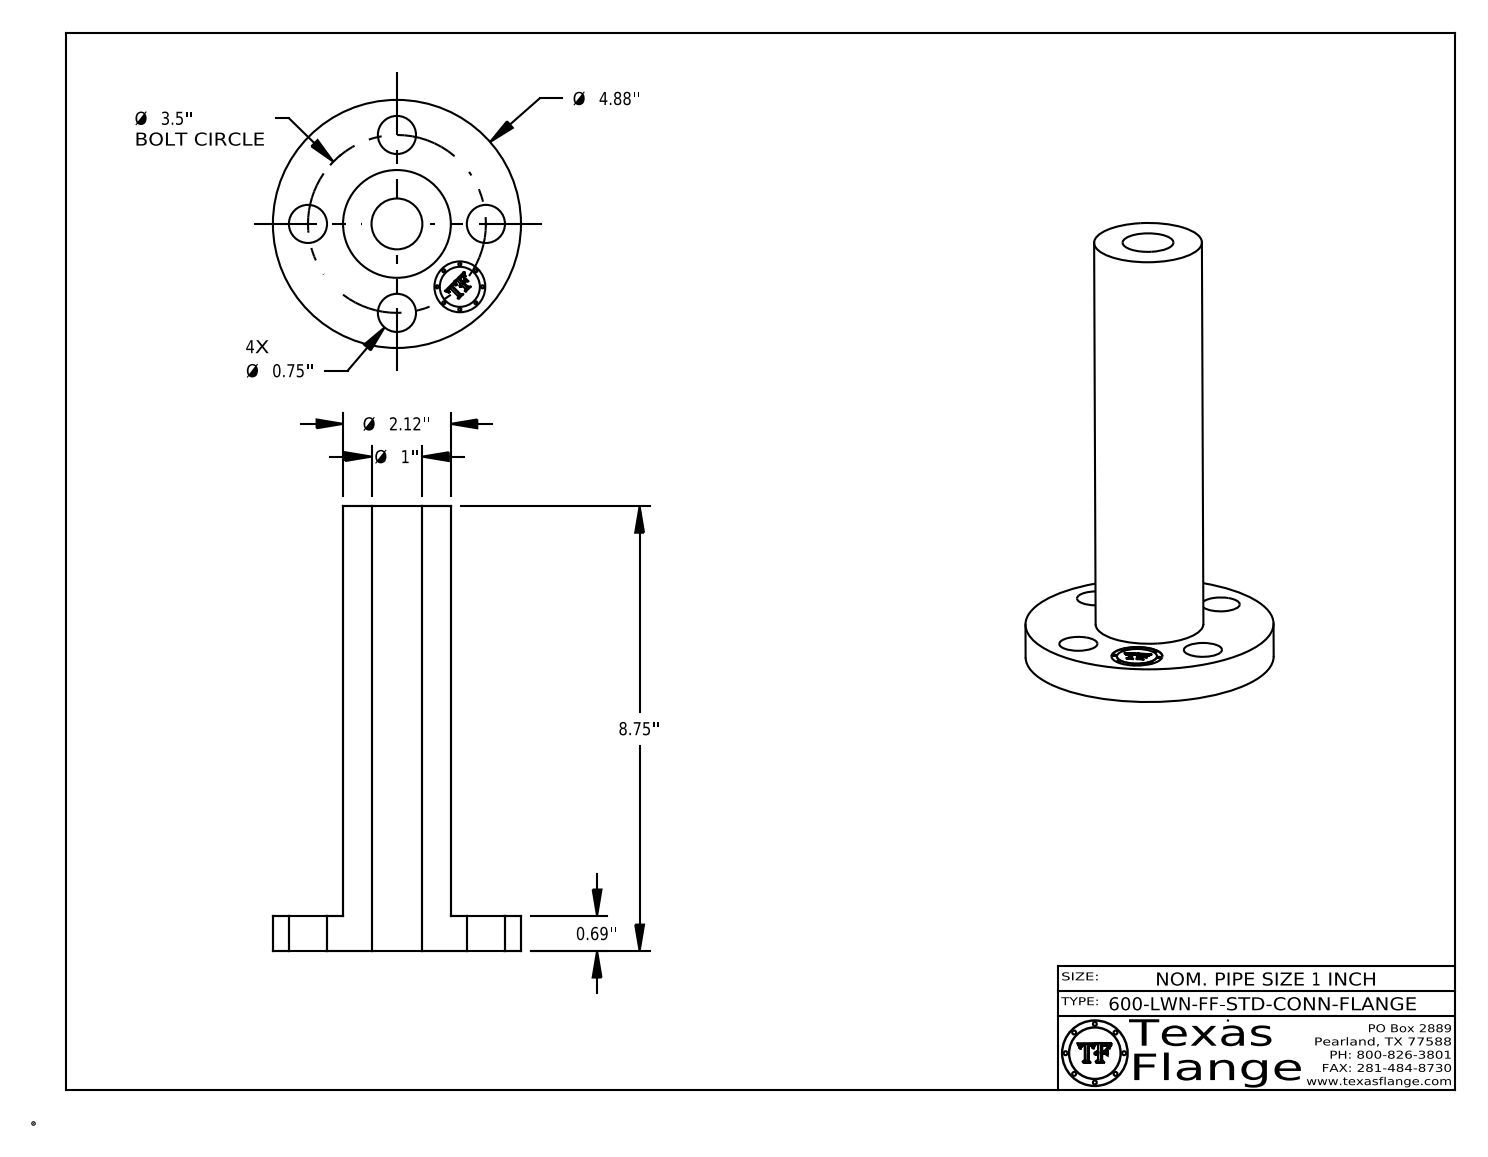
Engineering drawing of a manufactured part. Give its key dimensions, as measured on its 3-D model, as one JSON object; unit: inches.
{"part_name": "1-600-LWN-FF-STD-CONN-FLANGE", "step_written_by": "CATIA V5 STEP AP214 (AUTOMOTIVE_DESIGN)", "units": "inches", "bodies": {"solids": 1, "faces": 402, "planar": 368, "cylindrical": 34, "other": 0}, "overall_size": [8.75, 4.88, 4.88], "volume_in3": 33.26, "surface_area_in2": 130.6, "round_holes": [[0.75, 4], [1, 2]], "round_bosses_or_shafts": [[0.061, 8], [4.88, 1], [2.12, 1], [0.788, 1]], "face_to_face_distances": [0.69, 8.75, 8.06, 0.685, 8.065, 0.298, 0.293, 0.054, 0.193, 0.248], "hole_center_spacings": [1.75, 2.475, 1.339, 3.233, 3.5]}
